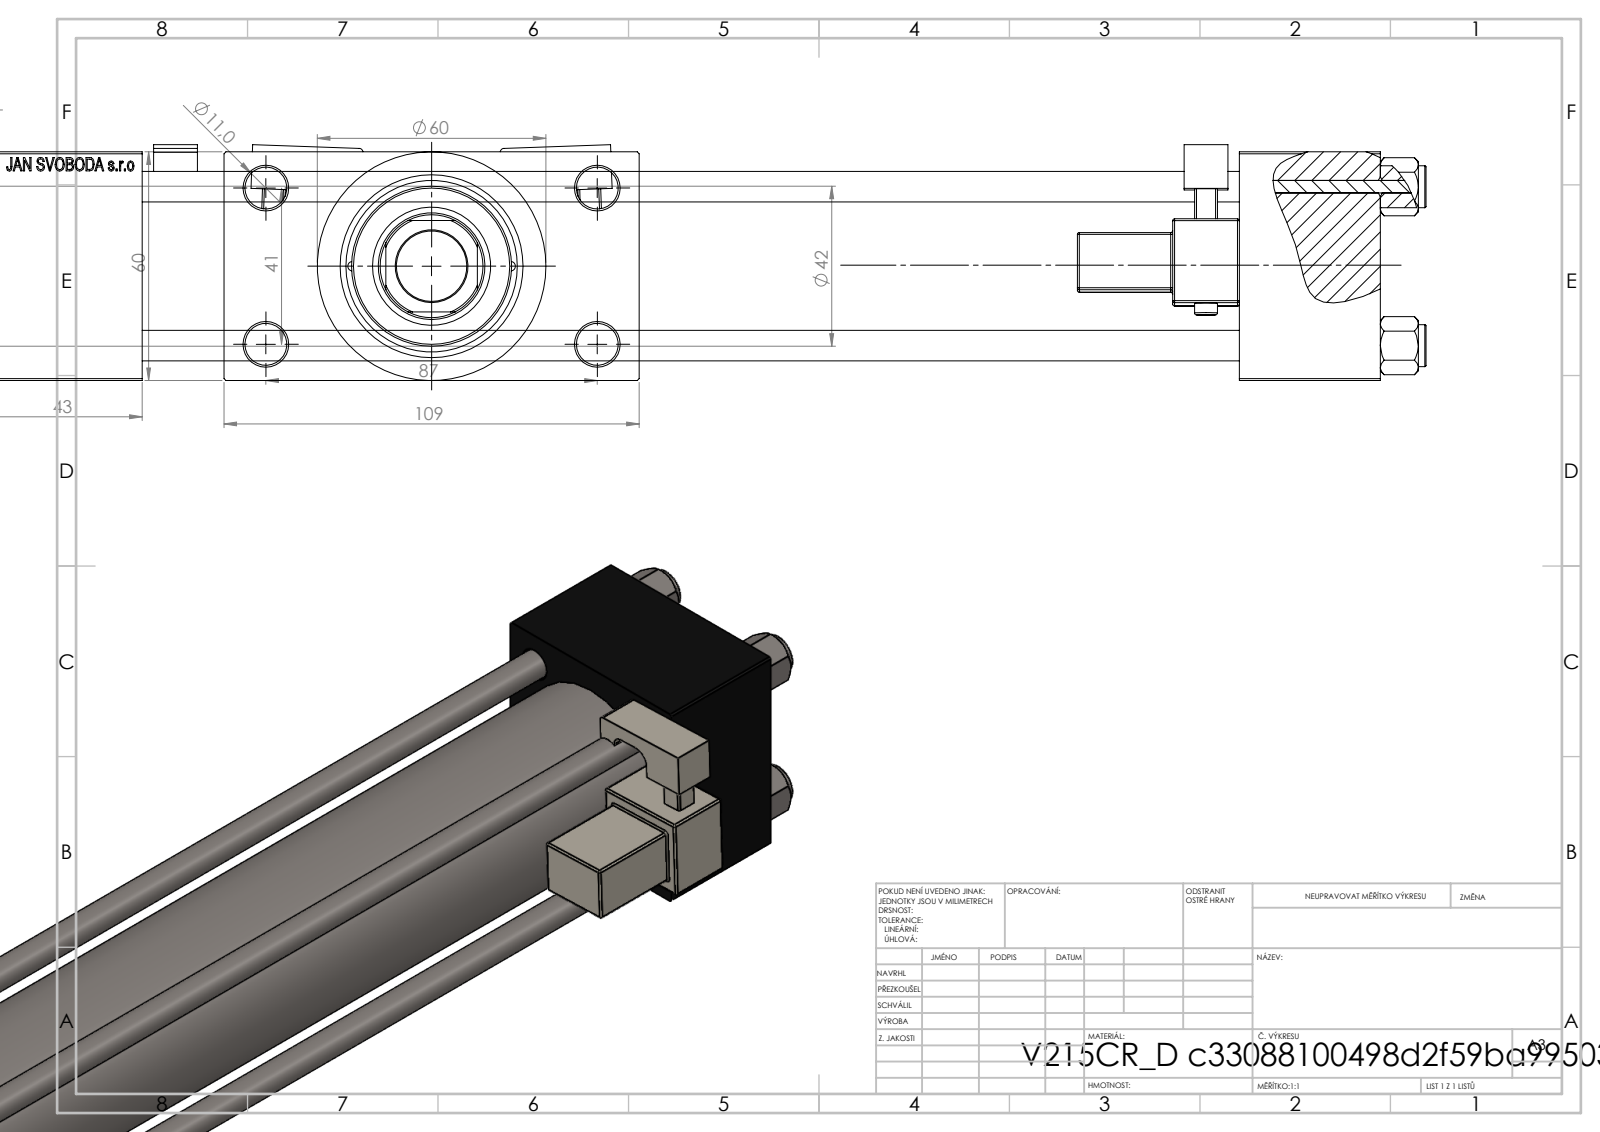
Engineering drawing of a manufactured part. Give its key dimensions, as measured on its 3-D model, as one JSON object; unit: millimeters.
{"part_name": "V215CR_D_Body; V215CR_MSU; V215CR_VCP_D; V215CR_D_TYCINKA (+2 more)", "step_written_by": "SolidWorks 2019 (CONFIG_CONTROL_DESIGN)", "units": "millimeters", "bodies": {"solids": 13, "faces": 1268, "planar": 560, "cylindrical": 152, "other": 556}, "overall_size": [415, 109, 61.9], "volume_mm3": 850579, "surface_area_mm2": 246658, "round_holes": [[8, 4], [11, 4], [2.5, 2], [7, 2], [16.66, 2], [24, 2], [18.5, 1], [28, 1], [31, 1], [40, 1], [45, 1]], "round_bosses_or_shafts": [[11, 4], [6, 2], [60, 1], [46, 1], [42, 1]], "partial_cylinders_radius": [[0.5, 48], [1, 2], [2.5, 2], [4, 2], [13.5, 1]], "face_to_face_distances": [60, 288, 24.5, 84.5, 37, 325, 368, 331, 43, 109], "hole_center_spacings": [20.85, 22.65, 29.49, 30.62, 41.7, 46.53, 47.15, 48.09]}
